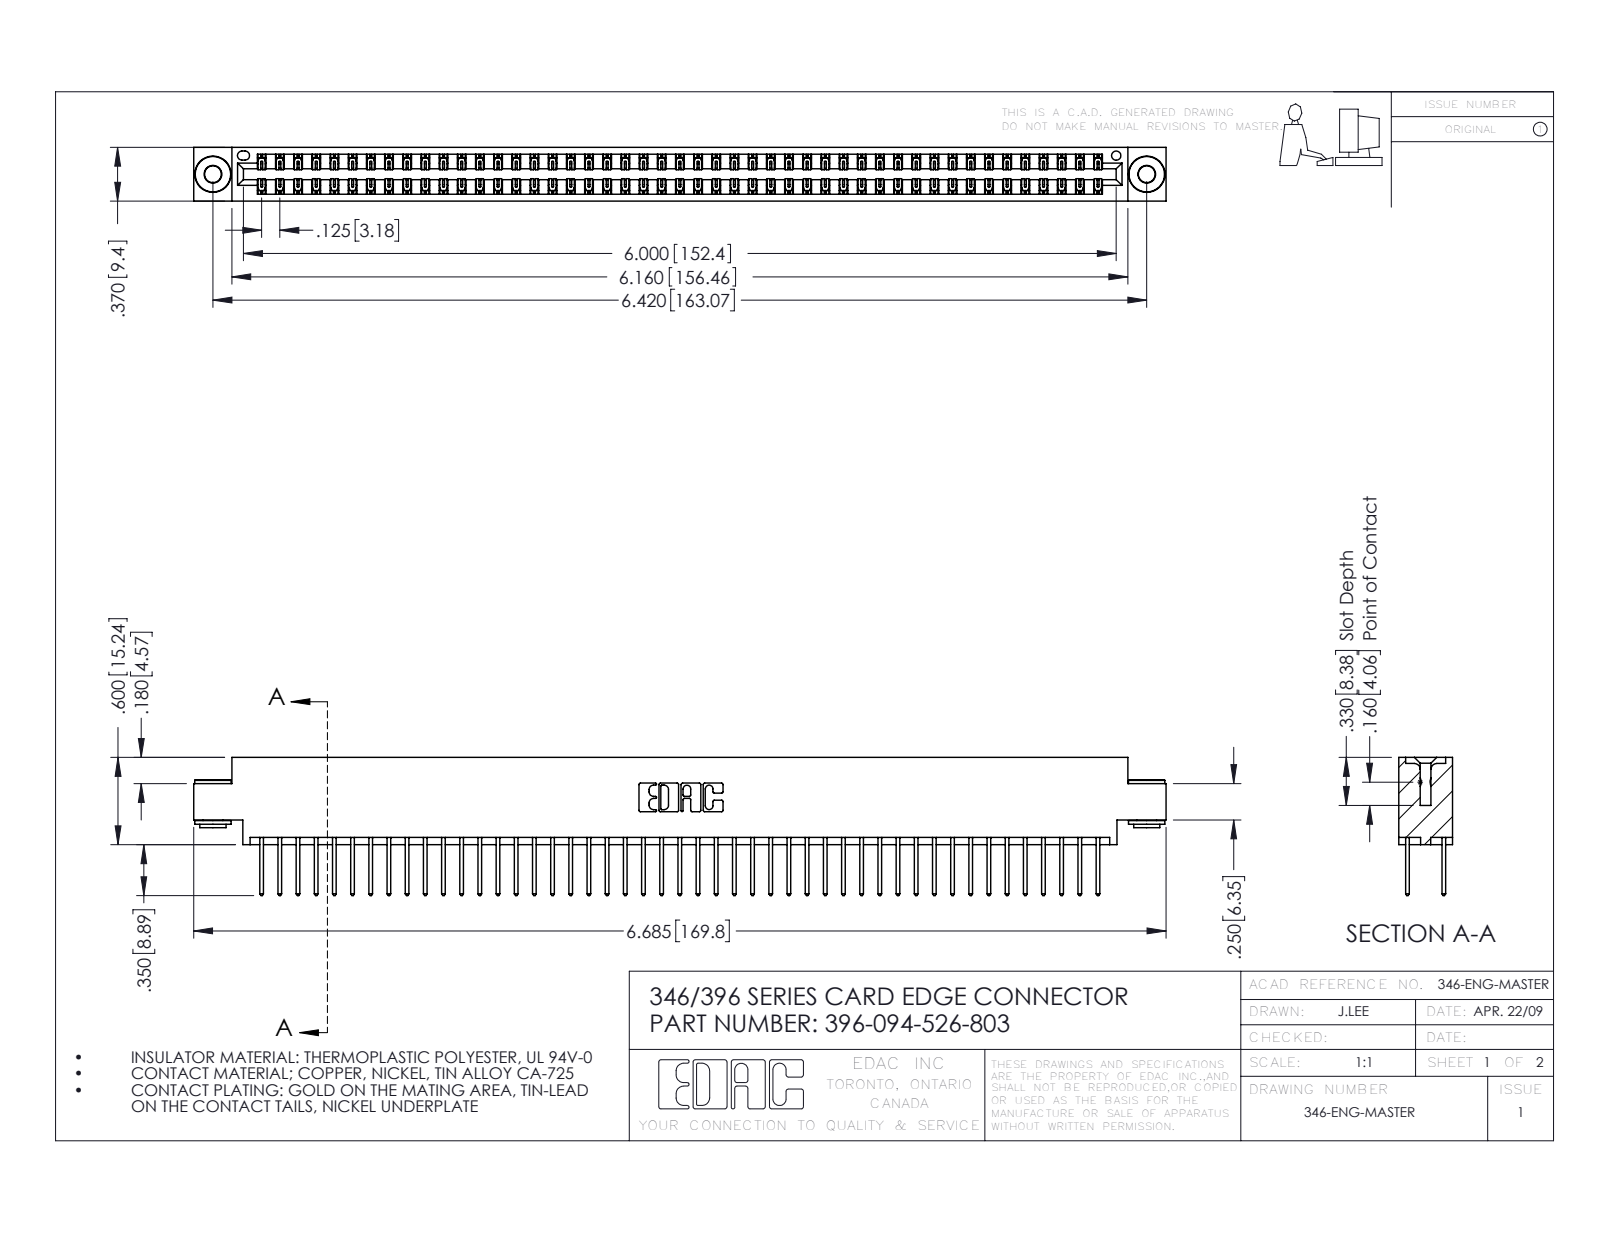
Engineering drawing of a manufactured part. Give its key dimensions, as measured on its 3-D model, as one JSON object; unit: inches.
{"part_name": "345-292-001_345-293-126; 396-094-526-803; 346 Part_0.170 Offset - 0.156 Dia-TH; 345-250-002_345-250-002-102", "step_written_by": "SolidWorks 2016 (CONFIG_CONTROL_DESIGN)", "units": "inches", "bodies": {"solids": 97, "faces": 5052, "planar": 3380, "cylindrical": 1664, "other": 8}, "overall_size": [6.685, 0.95, 0.37], "volume_in3": 1.014, "surface_area_in2": 37.2, "round_holes": [[0.116, 2], [0.156, 2], [0.064, 1]], "round_bosses_or_shafts": [[0.25, 2], [0.18, 2], [0.136, 2]], "partial_cylinders_radius": [[0.006, 141], [0.01, 94], [0.01, 22], [0.007, 6], [0.031, 6], [0.026, 3], [0.014, 2], [0.022, 2]], "face_to_face_distances": [0.048, 0.322, 0.25, 0.37, 0.025, 0.072, 0.298, 0.275, 0.148, 0.222], "hole_center_spacings": [0.246, 6.211, 6.42]}
